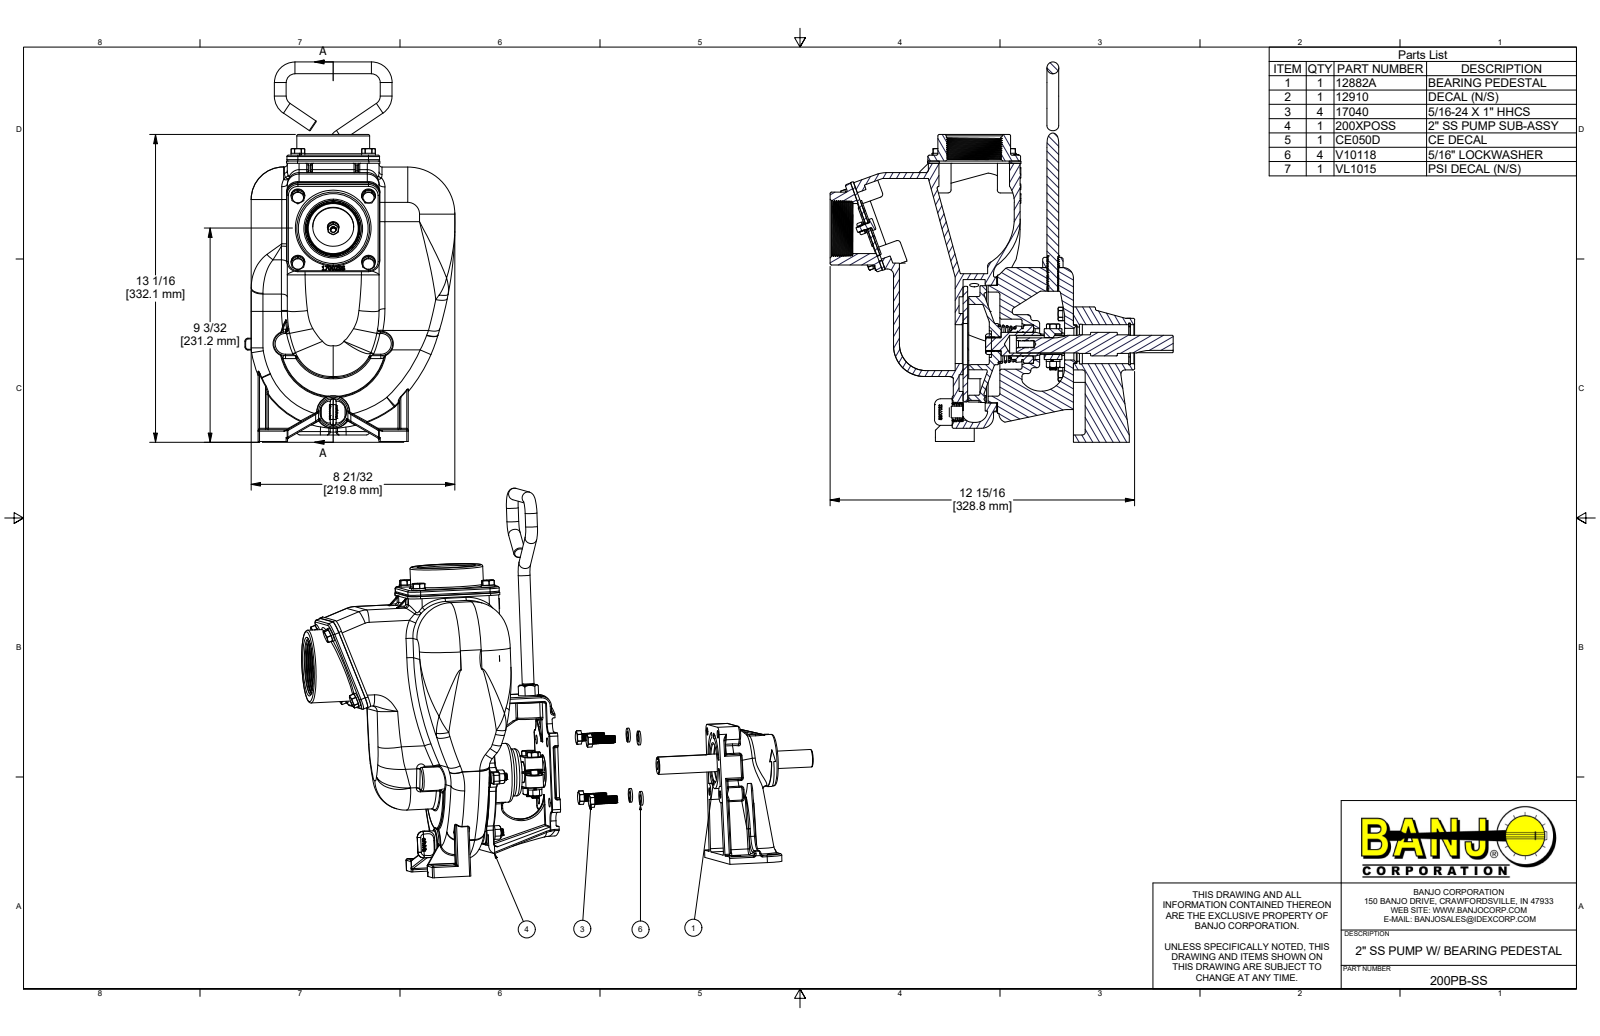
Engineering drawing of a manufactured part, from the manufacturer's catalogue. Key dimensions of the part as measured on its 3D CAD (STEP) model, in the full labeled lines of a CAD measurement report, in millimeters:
Part name (STEP PRODUCT): 200PB-SS; 200XPOSS; 200XPOSSL; 17026SS (+8 more)
STEP written by: Autodesk Inventor 2019 (AUTOMOTIVE_DESIGN)
Units: millimetres
Bodies: 78 solids, 7243 faces (1309 planar, 2569 cylindrical, 3365 other)
Overall size (bounding box): 1050.3 × 370.3 × 226.6
Volume: 2 787 000 mm³ · Surface area: 1 117 000 mm²
Round holes (diameter × count): ⌀8.2 ×20, ⌀6.4 ×17, ⌀9.1 ×10, ⌀9.5 ×10, ⌀6.4 ×8, ⌀8 ×6, ⌀6.8 ×5, ⌀10.3 ×4, ⌀4.7 ×3, ⌀2 ×2, ⌀5 ×2, ⌀8.9 ×2
Round bosses / shafts (diameter × count): ⌀6.8 ×162, ⌀7 ×92, ⌀14.8 ×20, ⌀8 ×16, ⌀5.4 ×12, ⌀6.2 ×6, ⌀12.7 ×5, ⌀78.6 ×2
Partial cylindrical surfaces — rounded edges, fillets, slot ends (radius × count): R1.5 ×183, R0.8 ×69, R3.2 ×46, R6.4 ×44, R0.5 ×22, R12.7 ×22, R11.1 ×18, R11.9 ×16
Main face-to-face distances: 6.4, 8, 3.2, 92.7, 45.1, 37.2, 119.1, 81.9, 74, 8.7
Hole centre spacings: 76.2, 53.9, 50.7, 65.1, 107.8, 71.4, 71.5, 29.5
